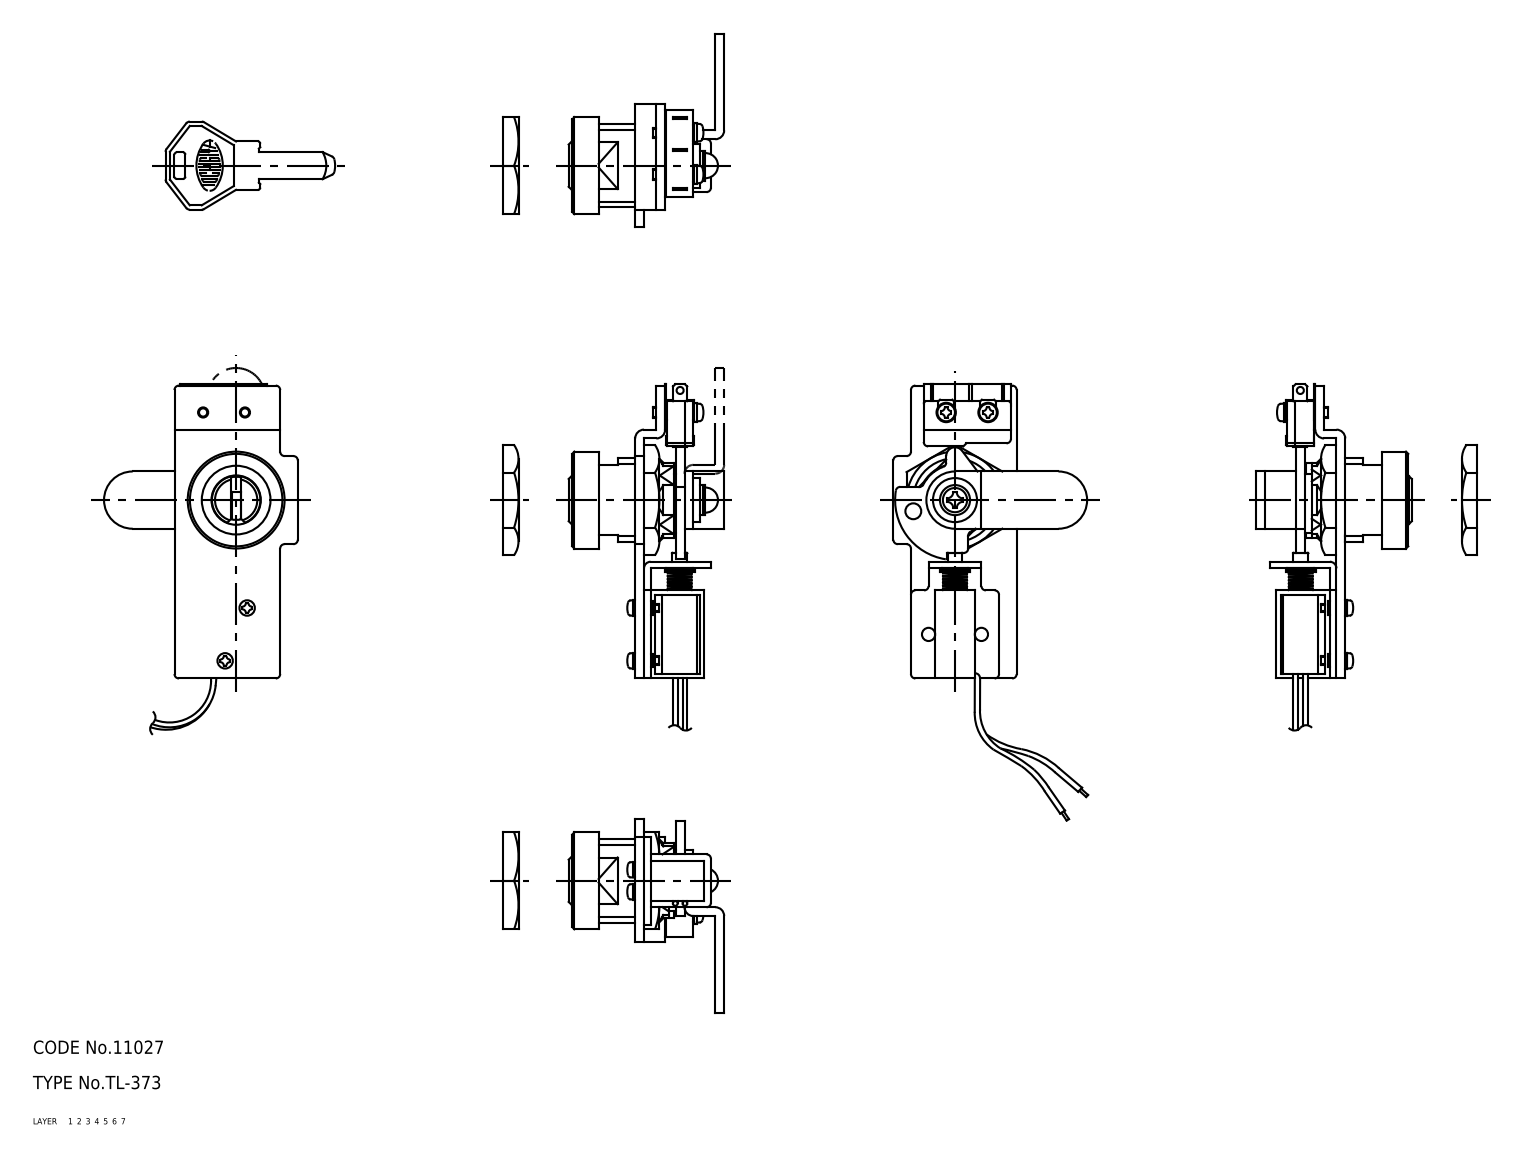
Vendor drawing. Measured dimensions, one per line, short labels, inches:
name: 67133353; 67133366; 67133379; 67133392 (+1 more)
written by: CADfix (AUTOMOTIVE_DESIGN)
unit: in
bodies: 5 solids, 461 faces (0 planar, 0 cylindrical, 461 other)
size: 4.152 × 3.894 × 1.732
volume: 1.038 in³; area: 21.65 in²
